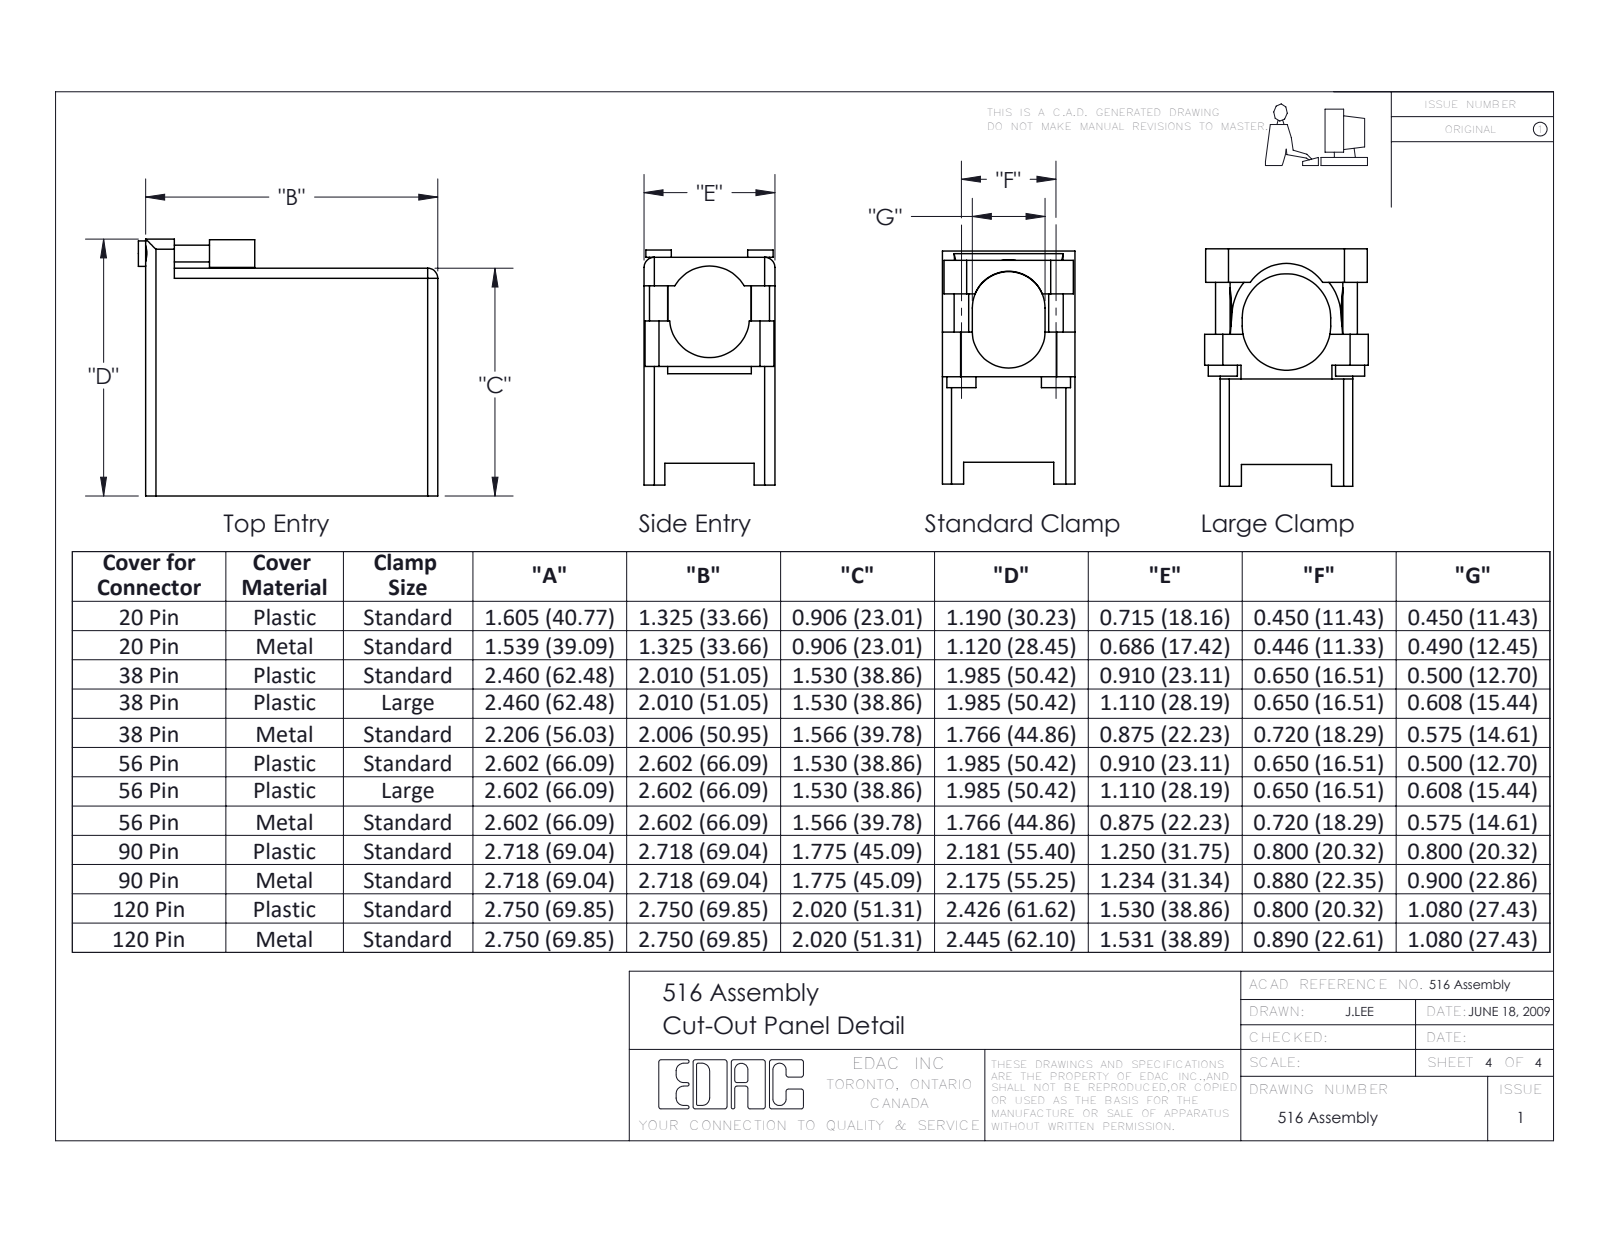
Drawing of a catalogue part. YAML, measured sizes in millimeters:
part_name: "516-020-501-566; 516-230-001_Metal - 020 Top Entry; 516 Plug Insulator_020; 516-292-001_501 Contact (+1 more)"
step_written_by: "SolidWorks 2020 (CONFIG_CONTROL_DESIGN)"
units: millimeters
bodies: {solids: 23, faces: 2172, planar: 1295, cylindrical: 741, other: 136}
overall_size: [42, 34.9, 18.2]
volume: 9140
surface_area: 16990
round_holes:
  - {diameter: 3.3, count: 20}
  - {diameter: 1.3, count: 10}
  - {diameter: 2.4, count: 5}
  - {diameter: 2.6, count: 2}
  - {diameter: 3, count: 2}
  - {diameter: 1.8, count: 1}
  - {diameter: 2.7, count: 1}
  - {diameter: 3.3, count: 1}
  - {diameter: 4.4, count: 1}
  - {diameter: 5.2, count: 1}
round_bosses_or_shafts:
  - {diameter: 2.2, count: 2}
  - {diameter: 3.7, count: 1}
  - {diameter: 3.7, count: 1}
  - {diameter: 3.2, count: 1}
partial_cylinders:
  - {radius: 0.6, count: 60}
  - {radius: 0.2, count: 40}
  - {radius: 0.3, count: 40}
  - {radius: 0.4, count: 40}
  - {radius: 0.3, count: 22}
  - {radius: 0.2, count: 20}
  - {radius: 0.5, count: 20}
  - {radius: 2, count: 20}
face_to_face_distances: [1.3, 3.8, 7.1, 16.9, 0.6, 3.3, 6.5, 3.2, 13.3, 2.9]
hole_center_spacings: [3.8, 3.8, 7.4, 11.1, 11.4, 7.6, 3.8, 6.6]
